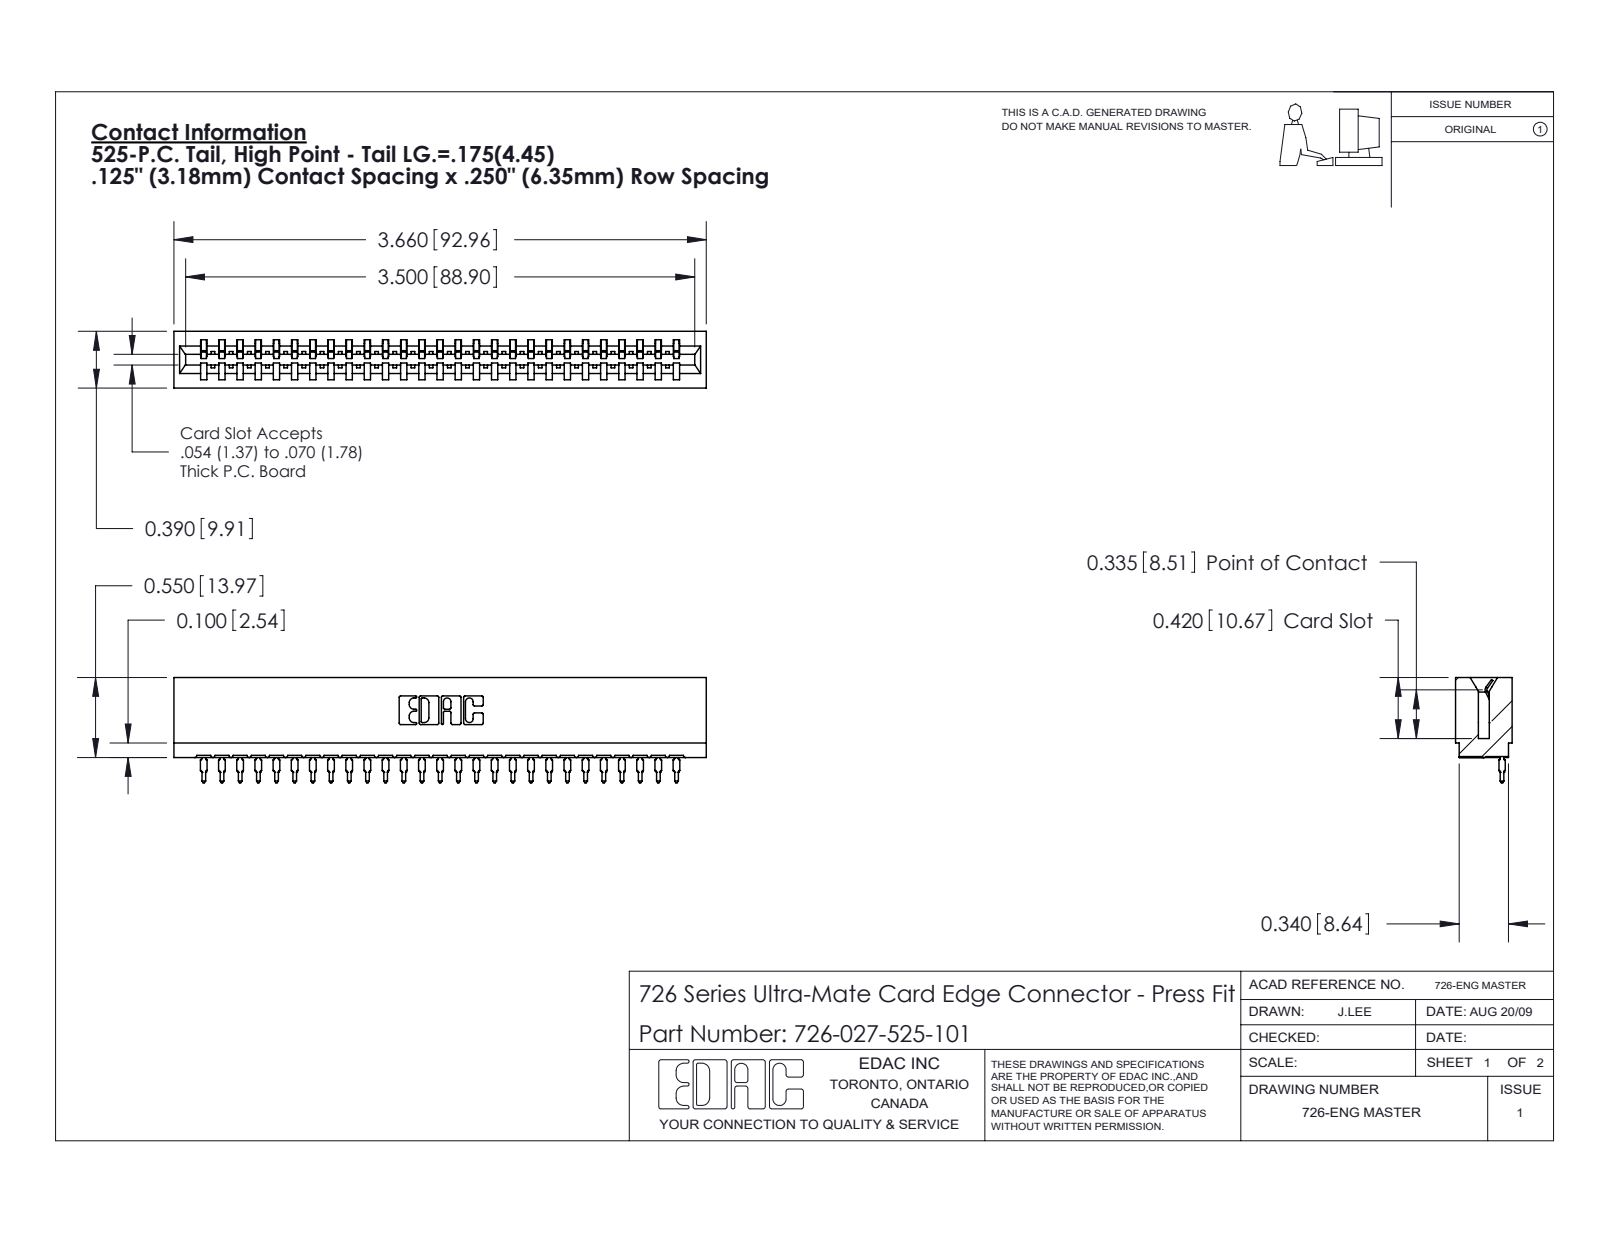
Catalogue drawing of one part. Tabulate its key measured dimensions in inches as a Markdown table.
| quantity | value |
| --- | --- |
| part name | 726 Part_.515 Slot Depth - 01; 726-027-525-101; 746-292-001_525 |
| STEP written by | SolidWorks 2020 (CONFIG_CONTROL_DESIGN) |
| units | inches |
| bodies | 28 solids, 3013 faces (1756 planar, 555 cylindrical, 702 other) |
| overall size | 3.66 × 0.724 × 0.39 |
| volume | 0.51 in³ |
| surface area | 19.22 in² |
| partial cylindrical surfaces (radius × count) | 0.021 × 54, 0.015 × 28, 0.01 × 22, 0.007 × 6, 0.031 × 6, 0.005 × 4, 0.011 × 4, 0.026 × 3 |
| main face-to-face distances | 0.057, 0.333, 0.39, 0.25, 0.025, 0.307, 0.083, 0.275, 0.5, 0.365 |
